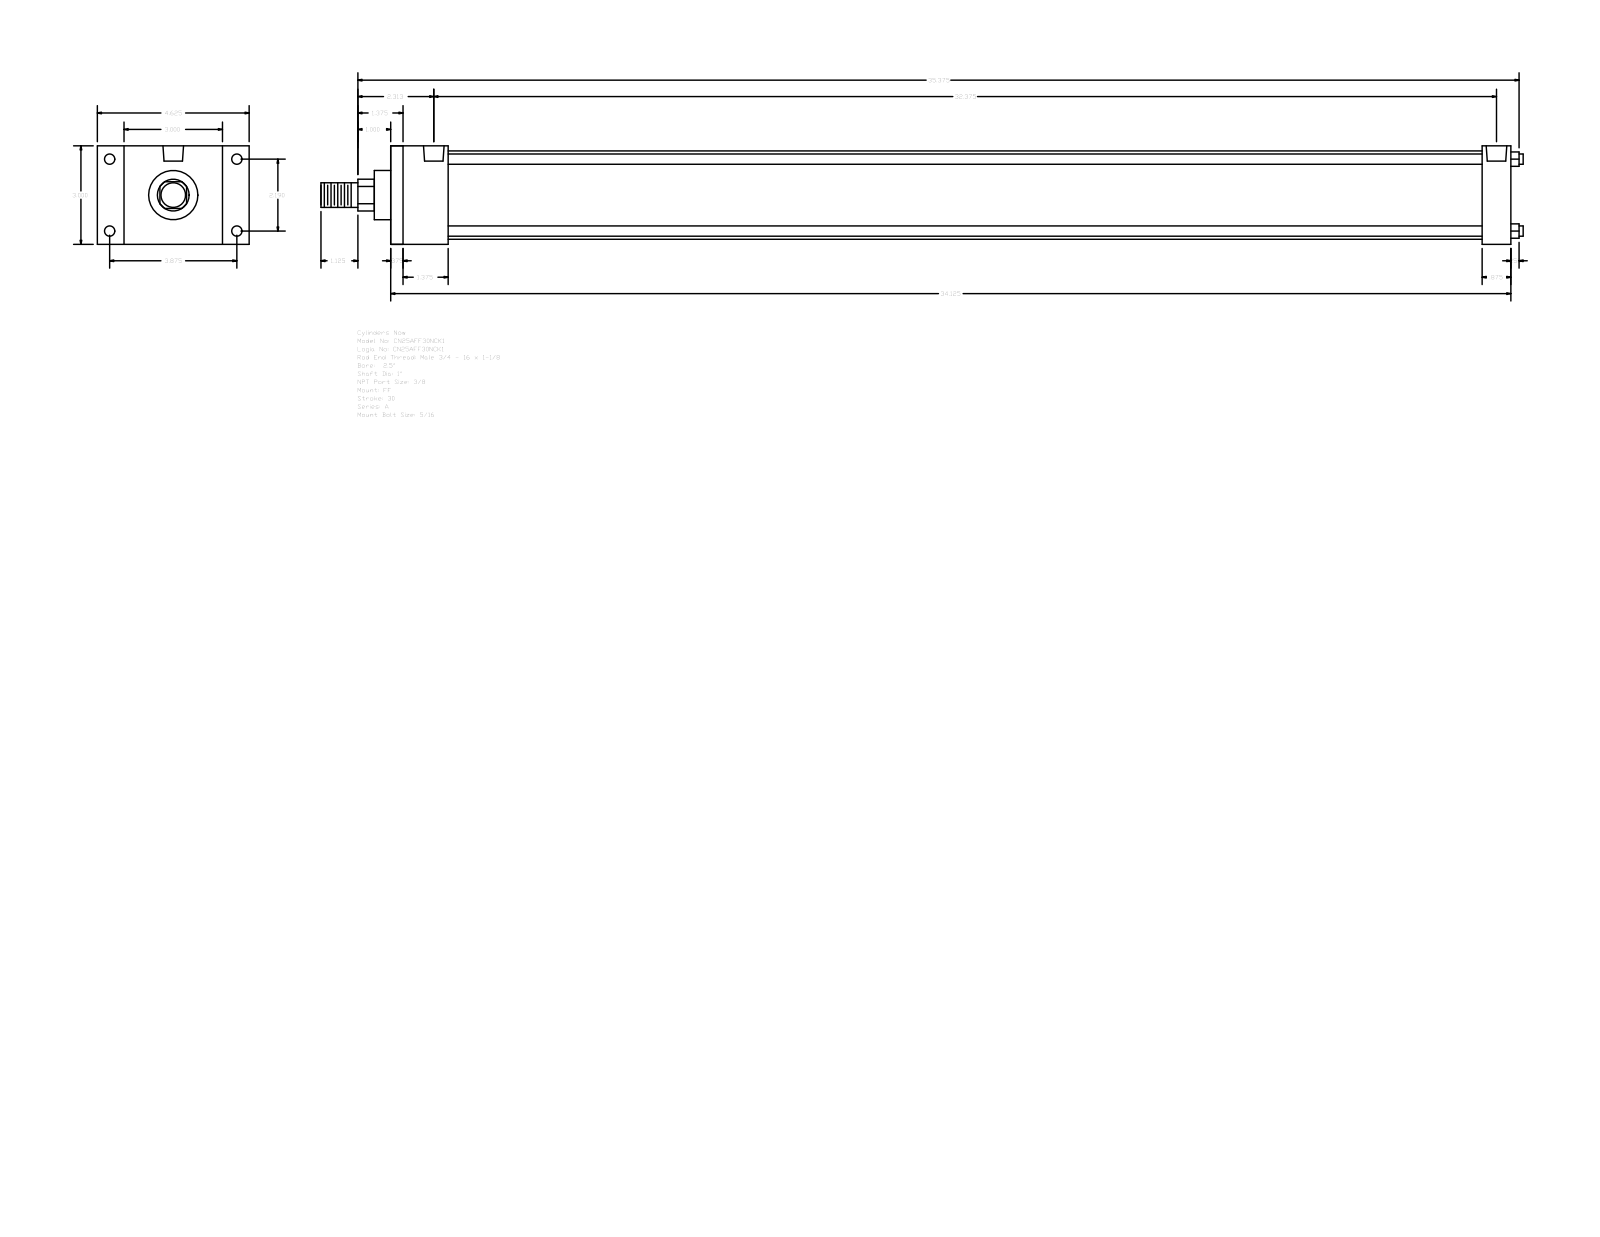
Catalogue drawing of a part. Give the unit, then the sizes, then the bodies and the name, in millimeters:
Units: millimetres
Overall size (bounding box): 930.27 × 117.47 × 76.2
Round holes (diameter × count): ⌀5.56 ×4, ⌀7.94 ×4, ⌀15.93 ×2
Round bosses / shafts (diameter × count): ⌀7.94 ×4, ⌀68.33 ×1, ⌀38.1 ×1, ⌀25.4 ×1, ⌀19.05 ×1
Partial cylindrical surfaces — rounded edges, fillets, slot ends (radius × count): R12.29 ×1
Main face-to-face distances: 76.2, 866.77, 857.25, 9.52, 22.22, 44.45, 844.55, 34.93, 835.03, 800.1
Hole centre spacings: 2.38, 55.62, 98.42, 113.05, 824.7, 827.08, 822.32
Bodies: 0 solids, 92 faces (64 planar, 28 cylindrical, 0 other)
Part name (STEP PRODUCT): A_FF__0250_1
STEP written by: GSSL Pune (CONFIG_CONTROL_DESIGN)
